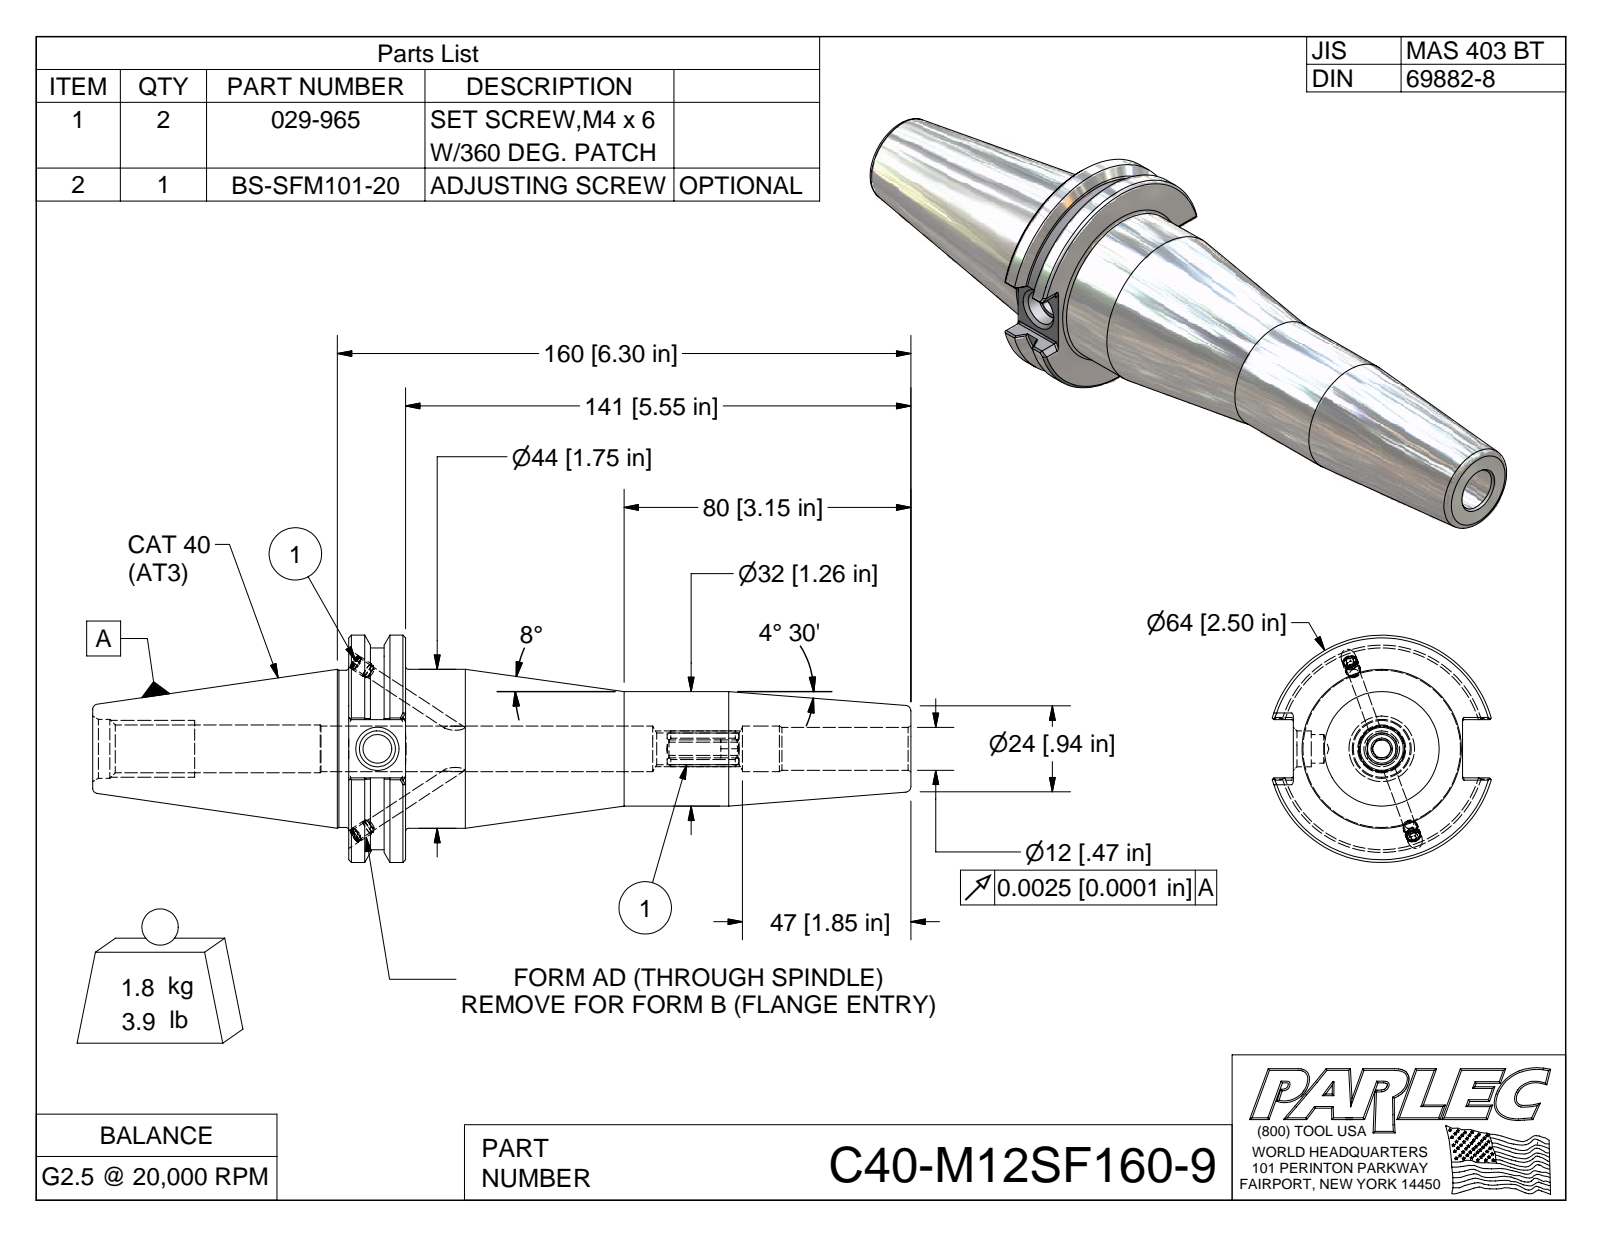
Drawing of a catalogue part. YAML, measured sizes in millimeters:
part_name: "C40-M12SF160-9; C40BC-M12SF160-9-1; 029-965; BS-SFM101-20"
step_written_by: "Autodesk Inventor 2009 (AUTOMOTIVE_DESIGN)"
units: millimeters
bodies: {solids: 4, faces: 154, planar: 65, cylindrical: 35, other: 54}
overall_size: [228.3, 63.5, 61.1]
volume: 217500
surface_area: 41340
round_holes:
  - {diameter: 3.3, count: 2}
  - {diameter: 4.1, count: 2}
  - {diameter: 12, count: 1}
  - {diameter: 12.7, count: 1}
round_bosses_or_shafts:
  - {diameter: 4.2, count: 2}
  - {diameter: 4, count: 2}
  - {diameter: 63.5, count: 1}
  - {diameter: 56.4, count: 1}
  - {diameter: 44.5, count: 1}
  - {diameter: 43.9, count: 1}
  - {diameter: 32, count: 1}
partial_cylinders:
  - {radius: 0.5, count: 12}
  - {radius: 5, count: 1}
face_to_face_distances: [15.9, 156.8, 141, 16.3, 47.2, 71.4, 87.3, 228.3, 6, 26.6]
